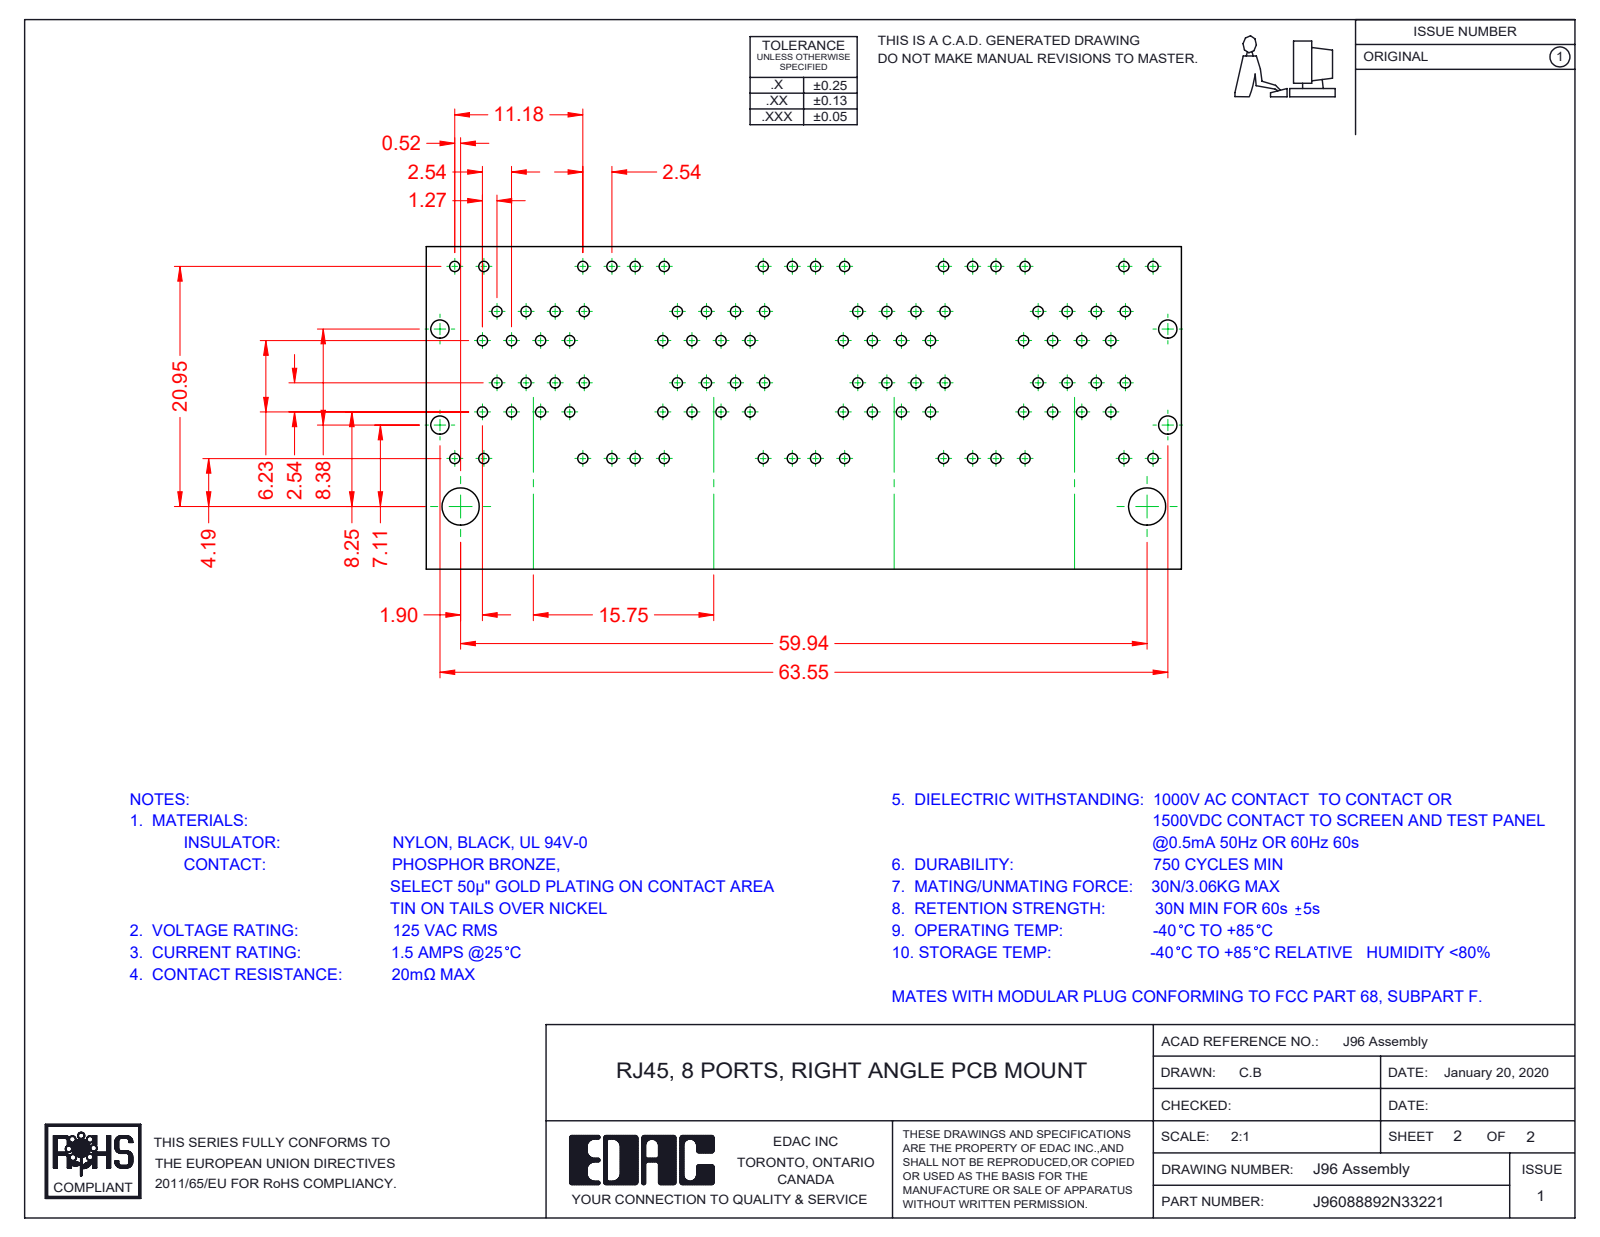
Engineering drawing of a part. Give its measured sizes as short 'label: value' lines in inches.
name: 96 LED LH Upper_3-Green; J96088892N33221; 96 Back Plate_8 Ports; 96 Contact Lock Lower (+8 more)
written by: SolidWorks 2016 (CONFIG_CONTROL_DESIGN)
unit: in
bodies: 96 solids, 7804 faces (6105 planar, 1388 cylindrical, 311 other)
size: 2.652 × 1.235 × 1.129
volume: 1.474 in³; area: 98.57 in²
holes: 3× ⌀0.067
bosses: 3× ⌀0.066
rounds: 124× R0.01, 73× R0.014, 72× R0.039, 49× R0.02, 32× R0.036, 27× R0.008, 14× R0.011, 11× R0.028
face distances: 0.62, 0.014, 0.392, 0.046, 0.063, 0.021, 0.393, 0.401, 0.499, 0.133
hole spacings: 0.62, 1.24
